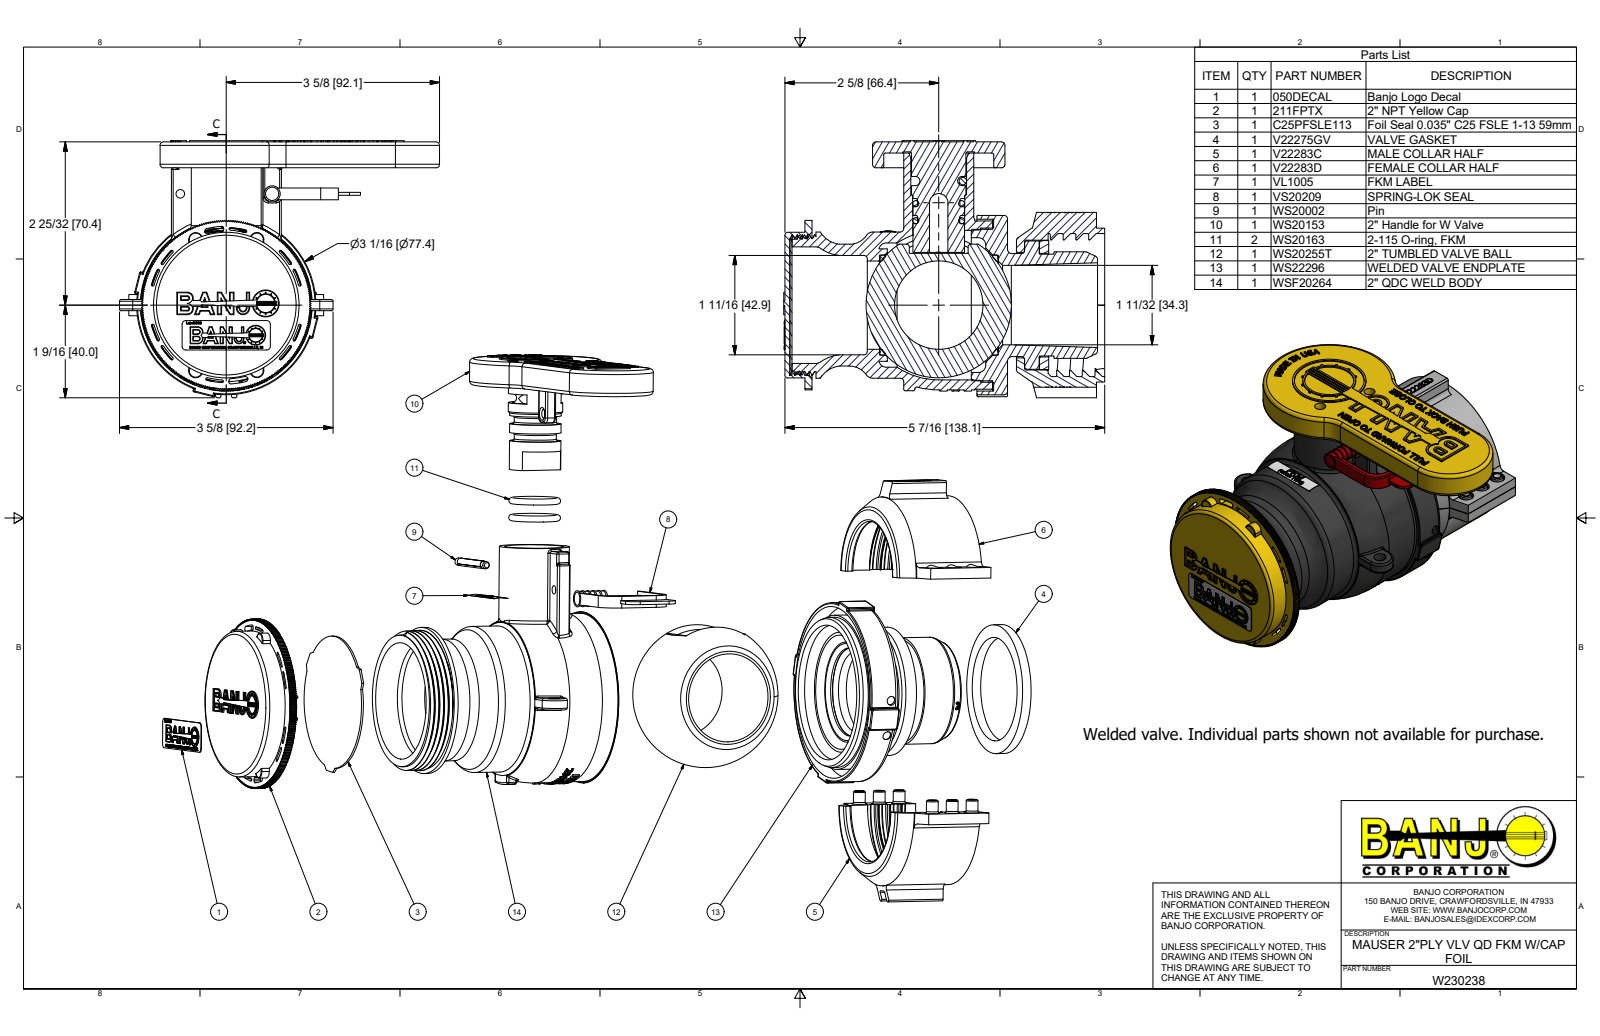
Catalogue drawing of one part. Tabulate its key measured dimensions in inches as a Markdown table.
| quantity | value |
| --- | --- |
| part name | W230238; WSF20264; WSF20264X; V22275GV (+8 more) |
| STEP written by | Autodesk Inventor 2018 (AUTOMOTIVE_DESIGN) |
| units | inches |
| bodies | 18 solids, 4819 faces (2543 planar, 996 cylindrical, 1280 other) |
| overall size | 5.456 × 5.44 × 4.368 |
| volume | 20.17 in³ |
| surface area | 256.4 in² |
| round holes (diameter × count) | 0.209 × 6, 0.257 × 6, 0.145 × 2, 0.15 × 2, 0.188 × 2, 0.207 × 2, 1.5 × 2, 0.156 × 1, 0.227 × 1, 0.309 × 1, 0.312 × 1, 0.321 × 1 |
| round bosses / shafts (diameter × count) | 0.2 × 6, 2.25 × 2, 3.047 × 1, 2.92 × 1, 2.91 × 1, 2.88 × 1, 2.858 × 1, 2.62 × 1 |
| partial cylindrical surfaces (radius × count) | 0.03 × 76, 0.015 × 24, 0.09 × 10, 0.06 × 4, 0.062 × 4, 0.118 × 4, 0.25 × 4, 0.01 × 3 |
| main face-to-face distances | 0.12, 0.085, 0.035, 0.19, 3.664, 3.699, 3.784, 0.25, 0.02, 0.54 |
| hole center spacings | 2.881, 2.857, 0.375, 0.375, 0.75, 1.633, 2.045, 2.237 |
